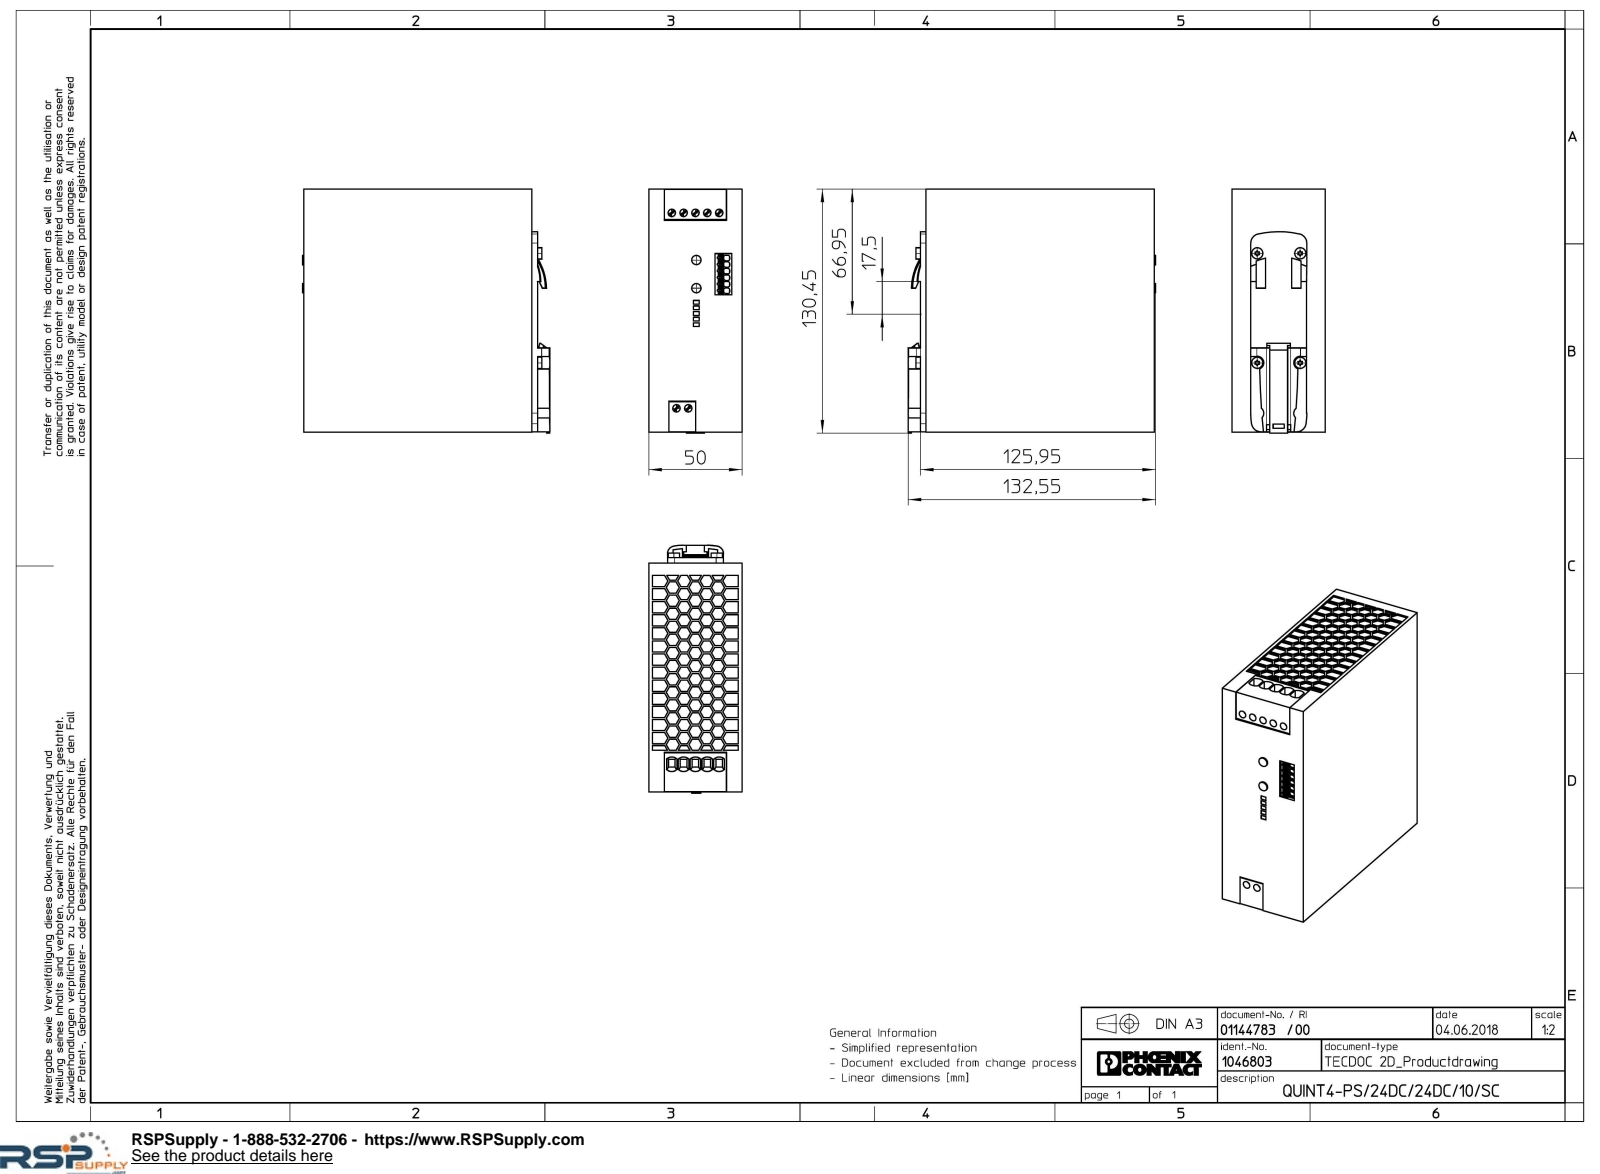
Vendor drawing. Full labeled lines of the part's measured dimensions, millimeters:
Part name (STEP PRODUCT): QUINT4_PS_24DC_24DC_10_SC-select
STEP written by: Creo Elements/Direct Modeling 20.1A 29-Sep-2018 (C) Parametric Technology GmbH (AUTOMOTIVE_DESIGN)
Units: millimetres
Bodies: 1 solid, 1942 faces (1774 planar, 138 cylindrical, 30 other)
Overall size (bounding box): 132.55 × 130.45 × 50
Volume: 801 690 mm³ · Surface area: 65 362 mm²
Round holes (diameter × count): ⌀4 ×7
Round bosses / shafts (diameter × count): ⌀6 ×4, ⌀5 ×2
Partial cylindrical surfaces — rounded edges, fillets, slot ends (radius × count): R0.1 ×48, R4 ×16, R0.97 ×12, R9.26 ×7, R0.57 ×6, R0.6 ×6, R3.5 ×4, R5 ×4
Main face-to-face distances: 50, 0.8, 129.2, 122.25, 128.4, 130, 3, 125.25, 3.5, 9.5
Hole centre spacings: 6.35, 12.7, 19.05, 104.53, 104.57, 104.99, 105.8, 25.4
